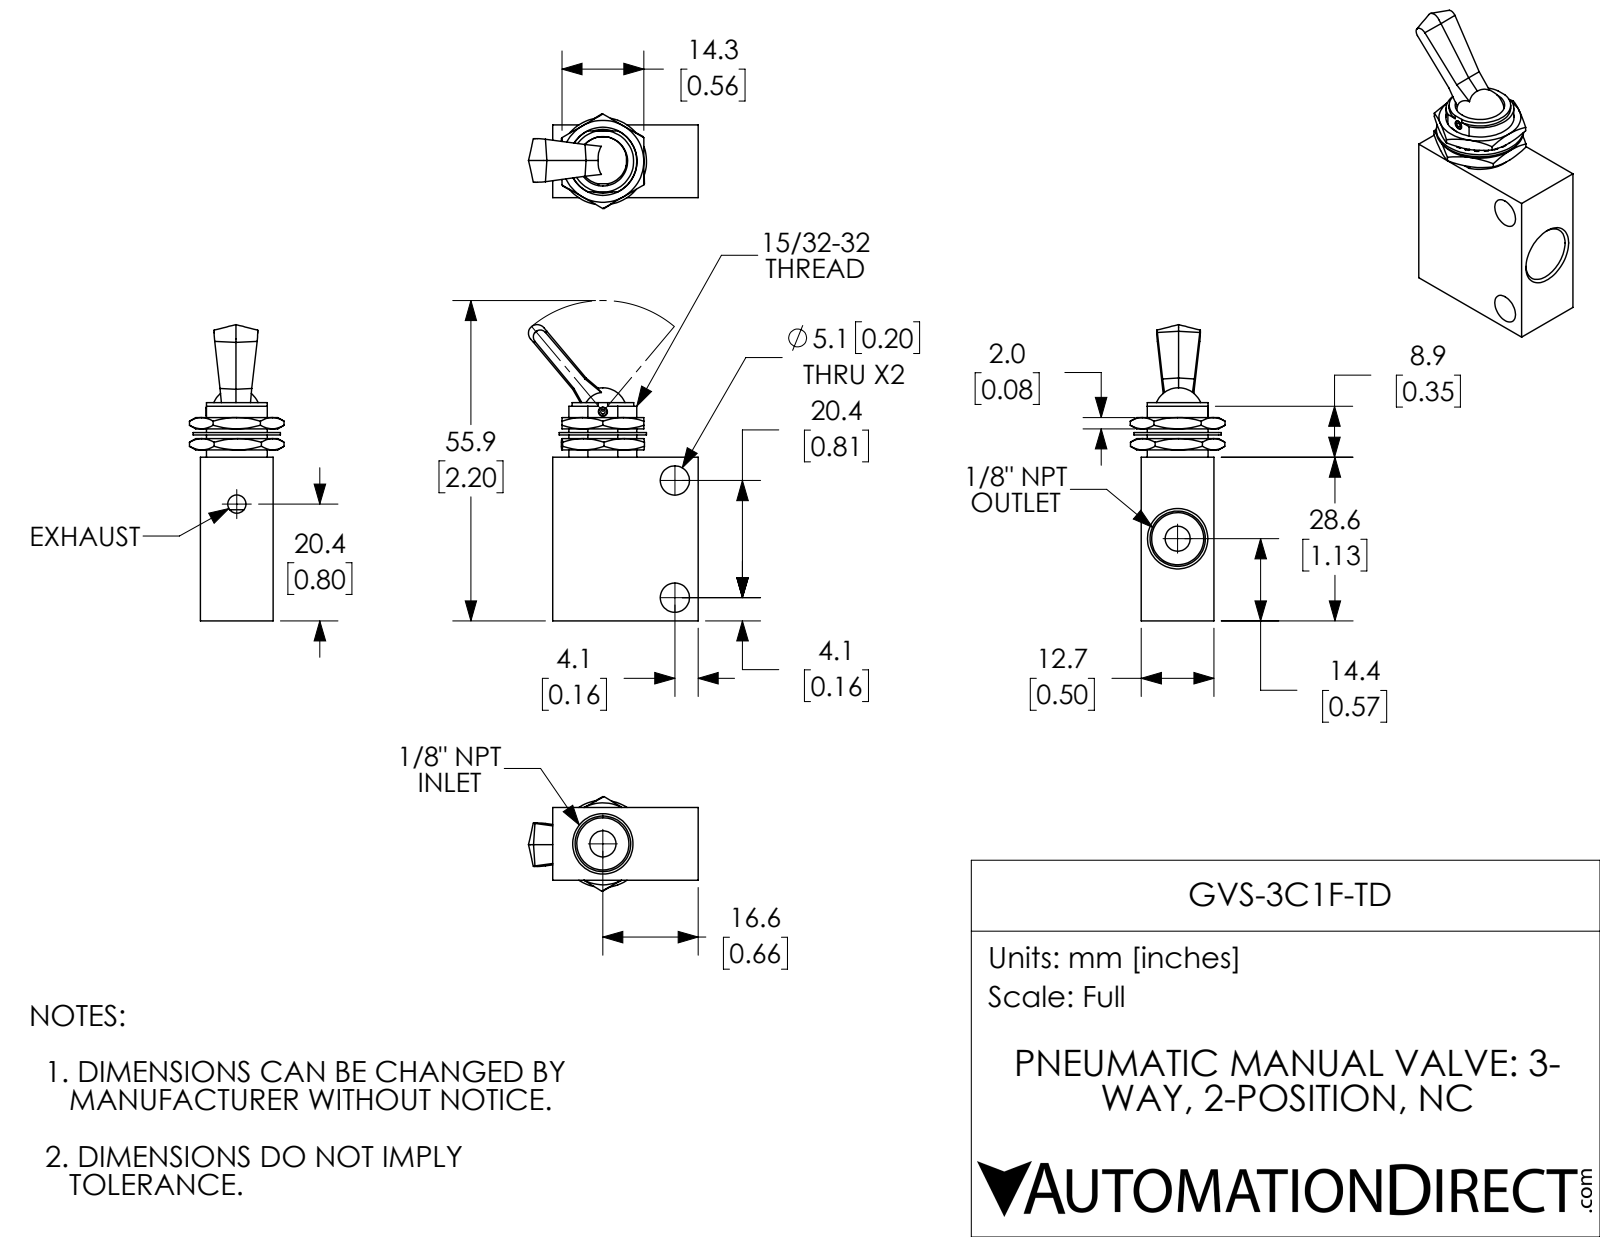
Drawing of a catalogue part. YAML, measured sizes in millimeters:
part_name: "GVS-3C1F-TD"
step_written_by: "SolidWorks 2018 (AUTOMOTIVE_DESIGN)"
units: millimeters
bodies: {solids: 6, faces: 235, planar: 96, cylindrical: 83, other: 56}
overall_size: [51.7, 29.6, 16.5]
volume: 7950
surface_area: 6023
round_holes:
  - {diameter: 5.1, count: 2}
  - {diameter: 0.8, count: 1}
  - {diameter: 1.6, count: 1}
  - {diameter: 1.8, count: 1}
  - {diameter: 3.2, count: 1}
  - {diameter: 4.4, count: 1}
  - {diameter: 4.6, count: 1}
  - {diameter: 6.4, count: 1}
  - {diameter: 8.6, count: 1}
  - {diameter: 11.1, count: 1}
round_bosses_or_shafts:
  - {diameter: 15.2, count: 1}
  - {diameter: 10.7, count: 1}
  - {diameter: 1.6, count: 1}
partial_cylinders:
  - {radius: 5.9, count: 1}
  - {radius: 6.1, count: 1}
  - {radius: 6.6, count: 1}
face_to_face_distances: [12.7, 25.4, 28.6, 3.7, 2, 1, 11.7, 1, 3, 2.6]
hole_center_spacings: [6, 17.4, 20.4, 34.8]
